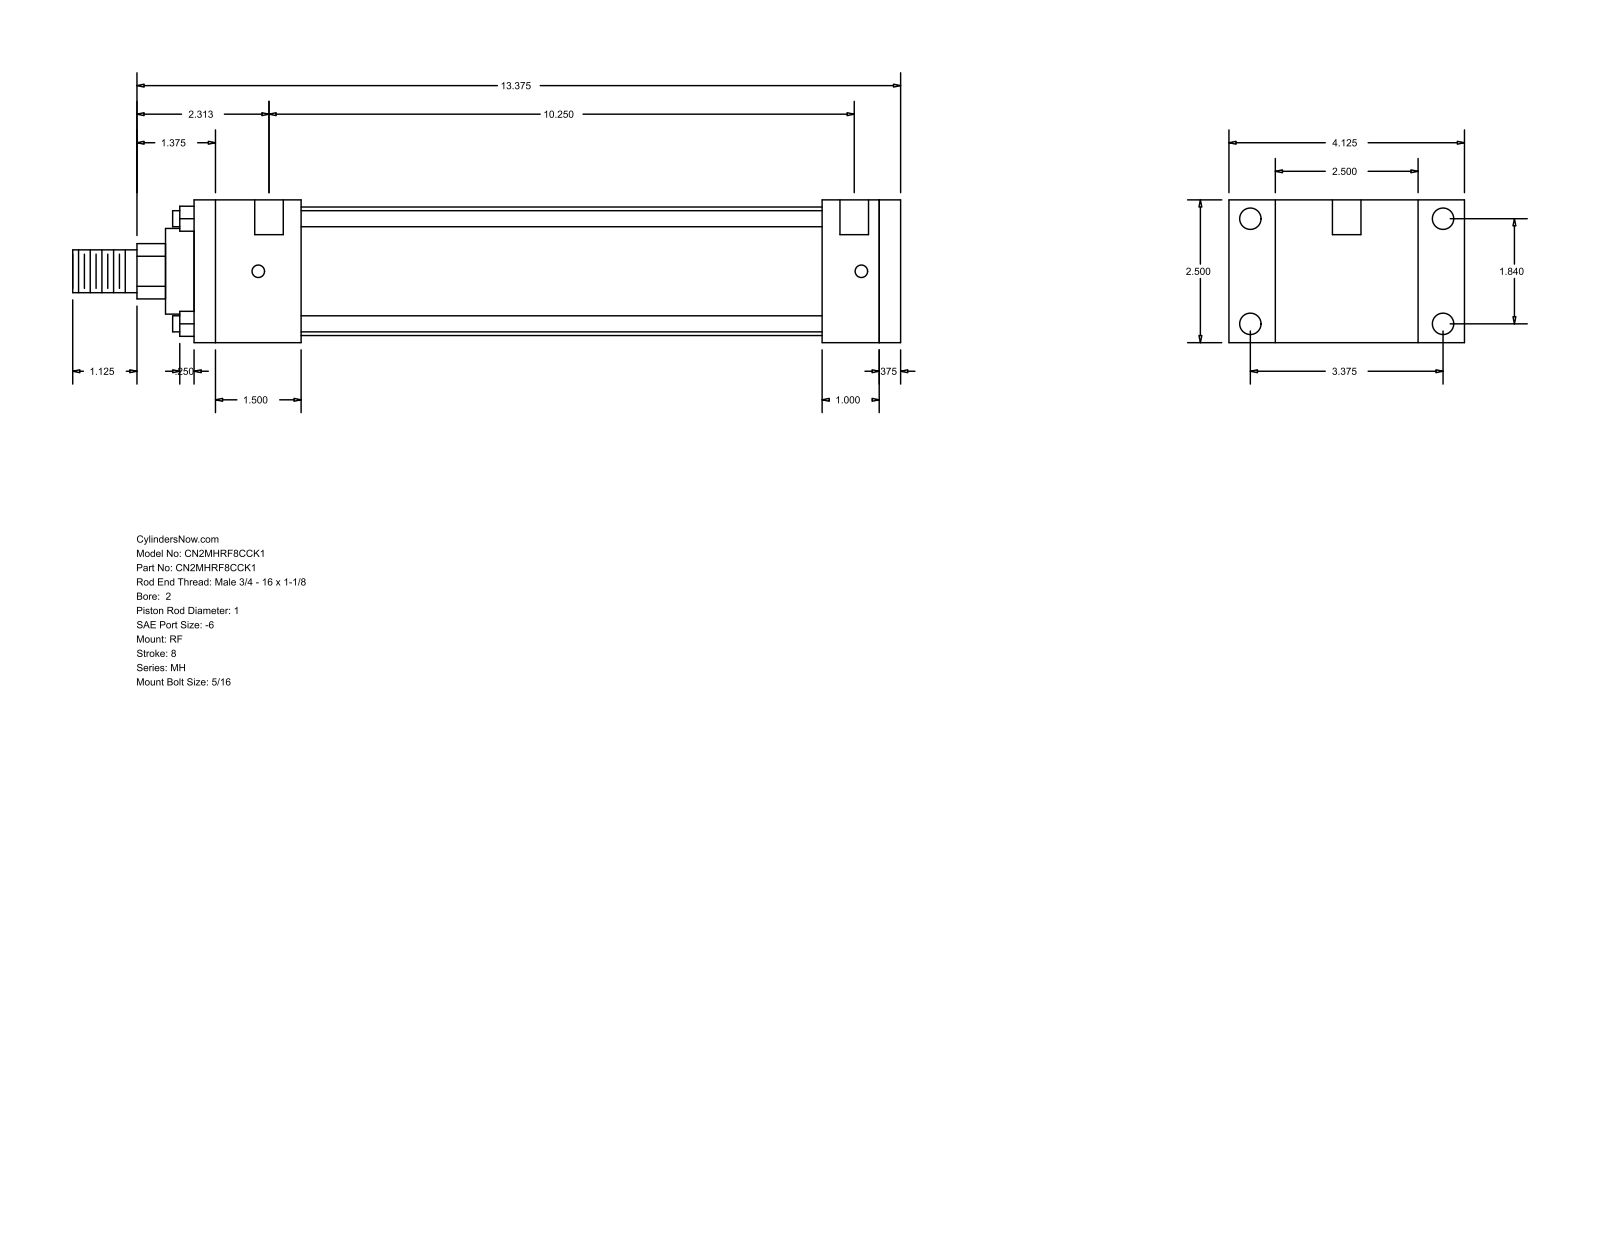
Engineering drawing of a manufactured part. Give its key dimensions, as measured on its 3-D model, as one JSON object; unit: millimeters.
{"part_name": "MH_RF__0200_1", "step_written_by": "GSSL Pune (CONFIG_CONTROL_DESIGN)", "units": "millimeters", "bodies": {"solids": 0, "faces": 92, "planar": 64, "cylindrical": 28, "other": 0}, "overall_size": [368.3, 104.78, 63.5], "round_holes": [[5.56, 4], [9.53, 4], [12.7, 2]], "round_bosses_or_shafts": [[7.14, 4], [57.15, 1], [38.1, 1], [25.4, 1], [19.05, 1]], "partial_cylinders_radius": [[12.29, 1]], "face_to_face_distances": [63.5, 314.33, 304.8, 9.53, 20.64, 25.4, 47.63, 279.4, 231.77, 257.17], "hole_center_spacings": [46.74, 85.72, 97.63, 268.28, 3.17, 4.76, 260.35, 263.52]}
